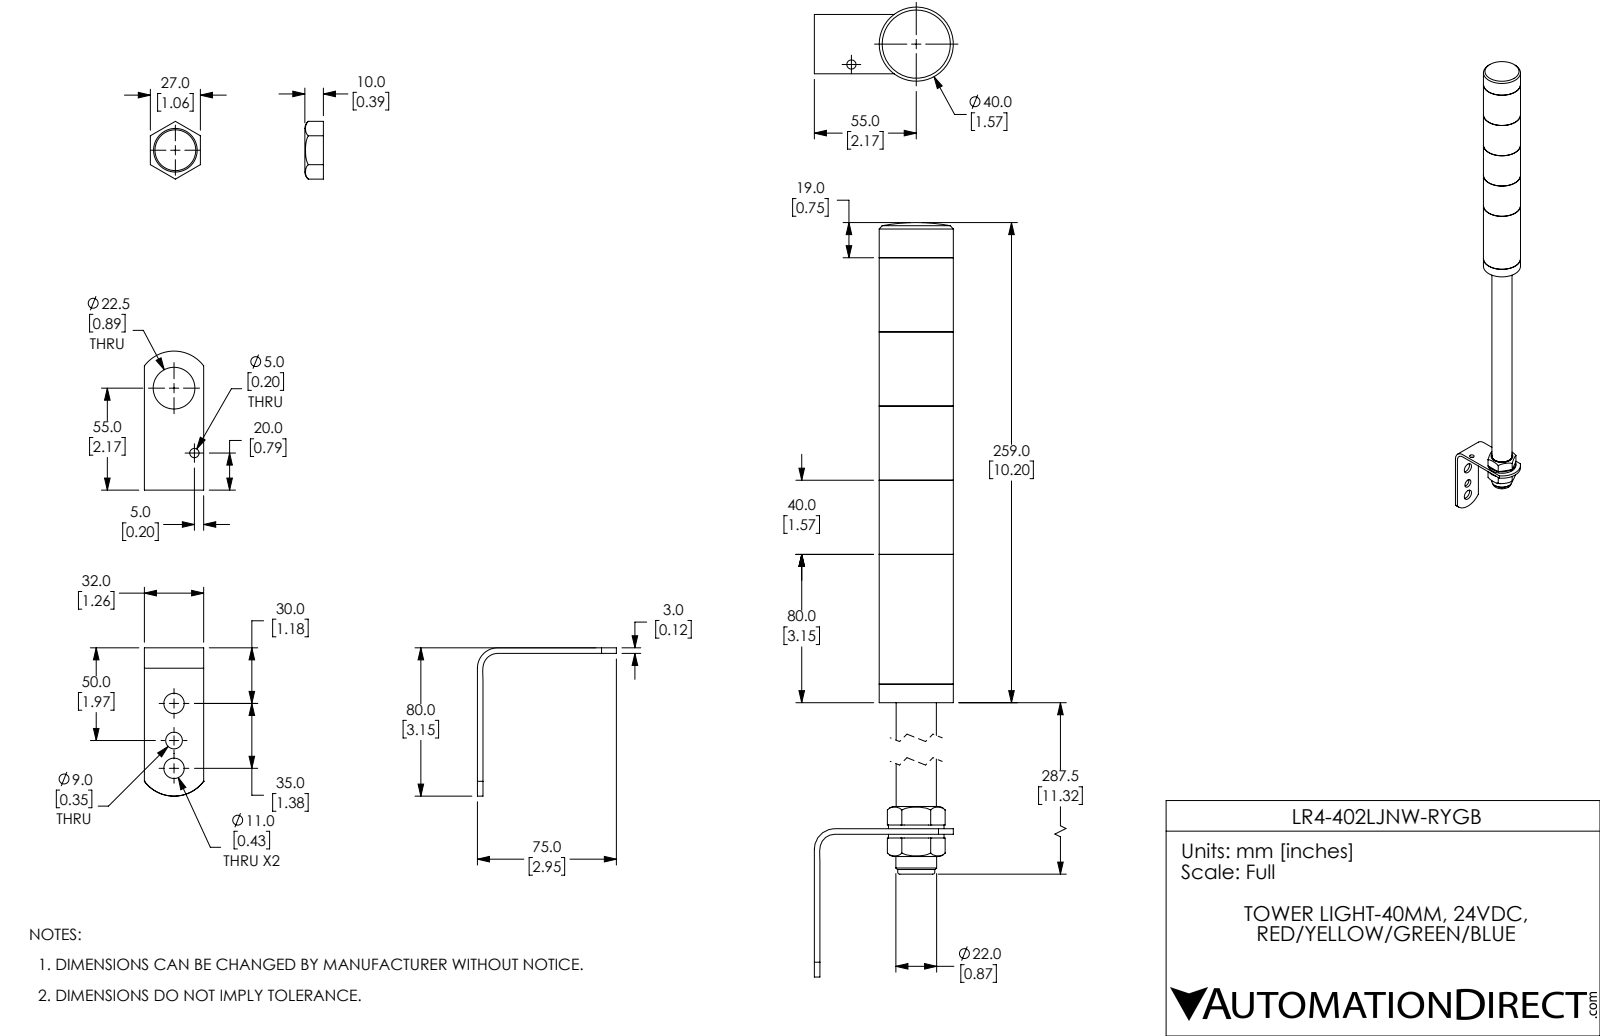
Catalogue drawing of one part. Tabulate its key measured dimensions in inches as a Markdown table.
| quantity | value |
| --- | --- |
| part name | LR4-402LJNW-RYGB |
| STEP written by | SolidWorks 2017 (AUTOMOTIVE_DESIGN) |
| units | inches |
| bodies | 13 solids, 178 faces (64 planar, 99 cylindrical, 15 other) |
| overall size | 23.7 × 2.953 × 1.575 |
| volume | 23.82 in³ |
| surface area | 189 in² |
| round holes (diameter × count) | 0.126 × 2, 0.433 × 2, 0.197 × 1, 0.303 × 1, 0.354 × 1, 0.697 × 1, 0.866 × 1, 0.886 × 1, 1.087 × 1, 1.366 × 1, 1.386 × 1, 1.39 × 1 |
| round bosses / shafts (diameter × count) | 1.575 × 1, 1.181 × 1, 0.854 × 1 |
| partial cylindrical surfaces (radius × count) | 0.787 × 1 |
| main face-to-face distances | 1.575, 3.15, 4.724, 6.299, 3.555, 0.406, 5.13, 1.98, 1.169, 2.598 |
| hole center spacings | 0.283, 0.567, 0.591, 0.787, 1.177, 1.378, 1.444, 1.717 |
